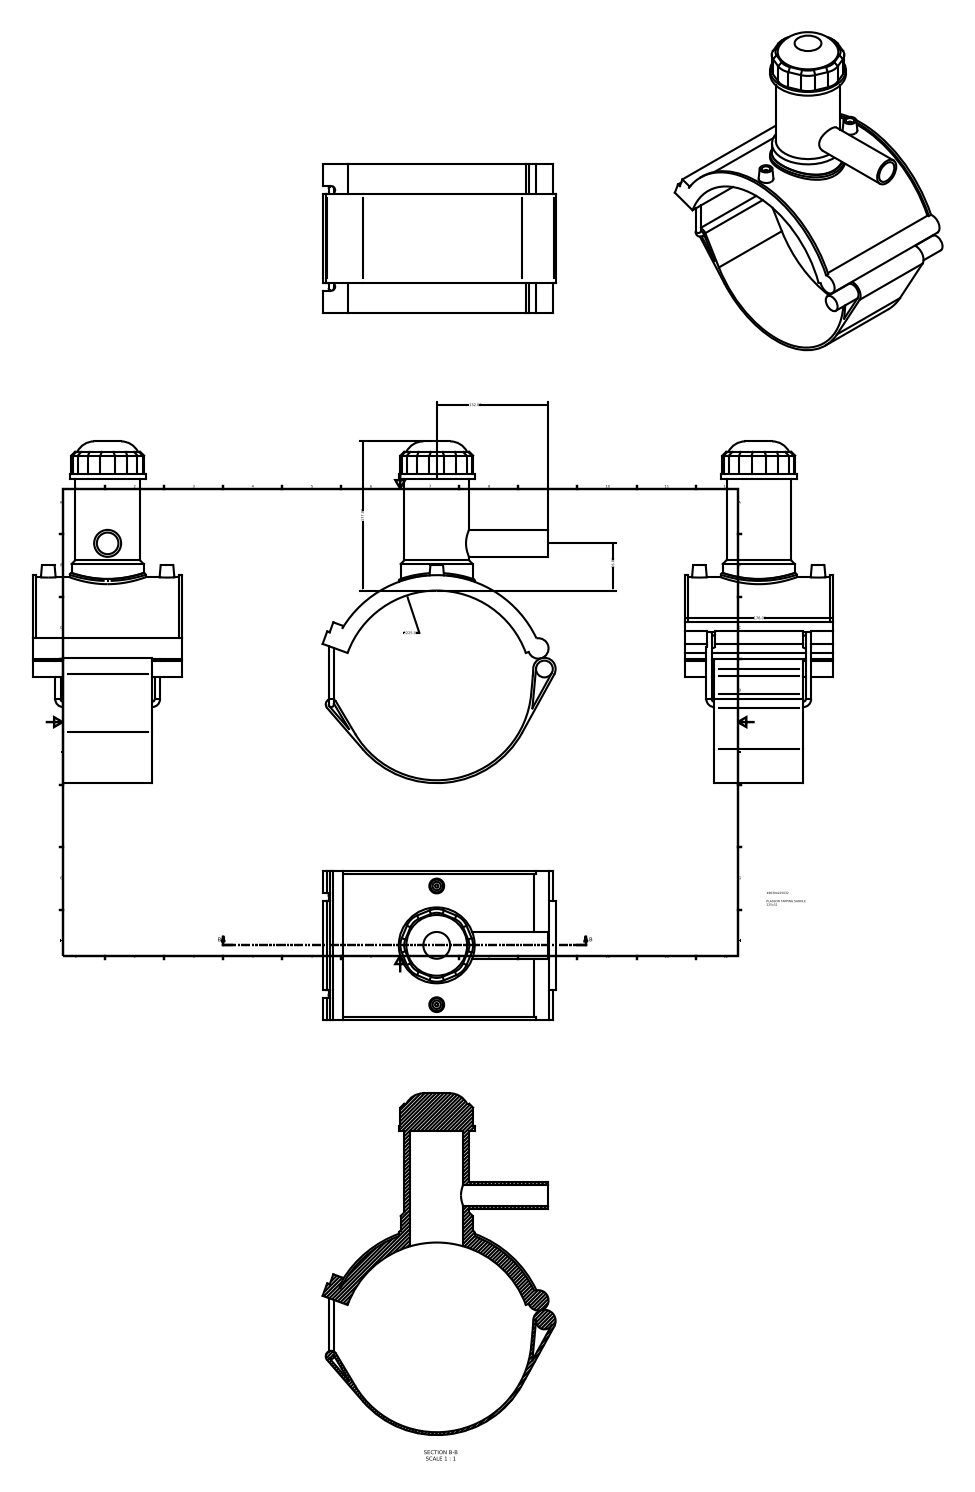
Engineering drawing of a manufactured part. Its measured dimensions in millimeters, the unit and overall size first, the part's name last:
Units: millimetres
Overall size (bounding box): 405.38 × 276.37 × 176
Round holes (diameter × count): ⌀10 ×2, ⌀25.6 ×1, ⌀63 ×1
Round bosses / shafts (diameter × count): ⌀6.3 ×2, ⌀4 ×2, ⌀90 ×1, ⌀85.5 ×1, ⌀76.5 ×1, ⌀32 ×1, ⌀19.9 ×1
Partial cylindrical surfaces — rounded edges, fillets, slot ends (radius × count): R22.5 ×8, R4.72 ×2, R112.5 ×2, R3.15 ×1, R6.53 ×1, R12.12 ×1, R13.33 ×1, R115.88 ×1
Main face-to-face distances: 176, 3.4, 3.38, 3.37, 35.2, 140.8, 3, 3.15, 28.35, 15.76
Hole centre spacings: 70.4, 140.8
Volume: 1 600 000 mm³ · Surface area: 343 622 mm²
Bodies: 1 solid, 121 faces (68 planar, 38 cylindrical, 15 other)
Part name (STEP PRODUCT): 496304225032
STEP written by: Autodesk Inventor 2015 (AUTOMOTIVE_DESIGN)
